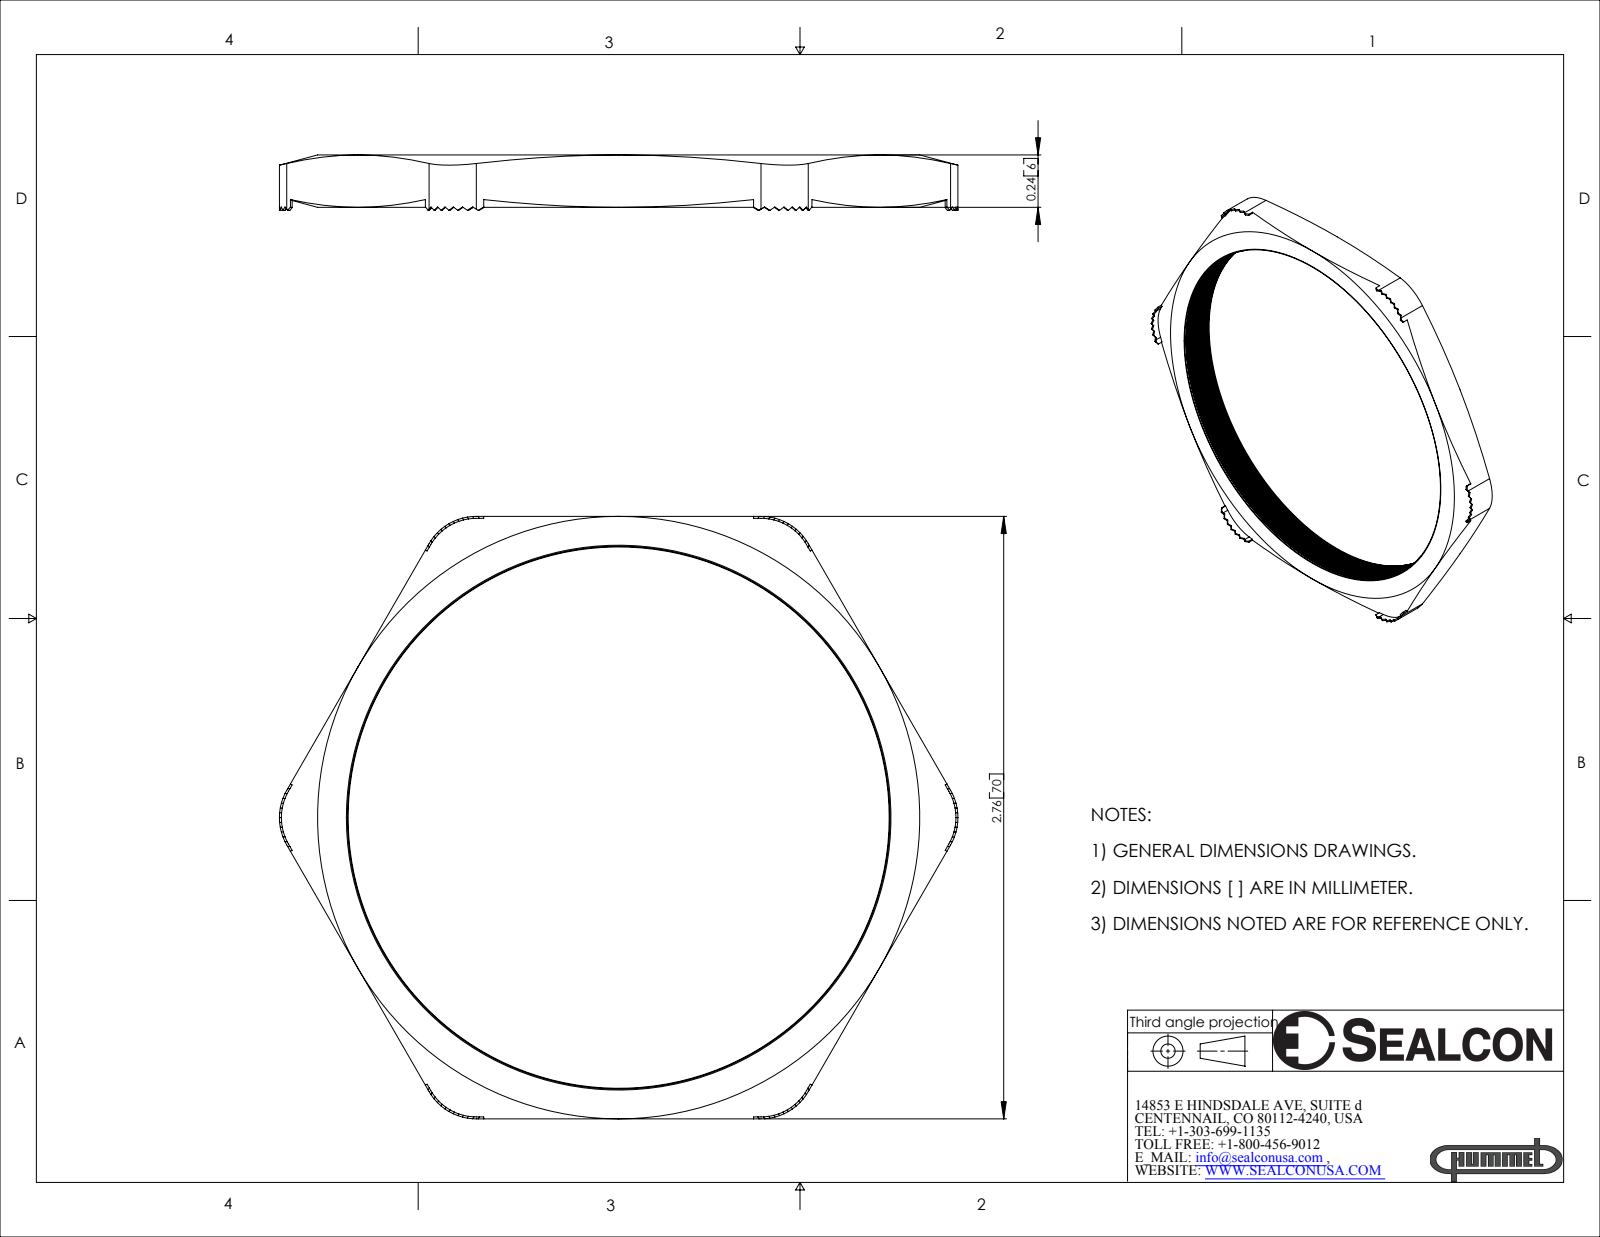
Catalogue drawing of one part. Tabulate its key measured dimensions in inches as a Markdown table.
| quantity | value |
| --- | --- |
| part name | NM-63-BE |
| STEP written by | SolidWorks 2007 (CONFIG_CONTROL_DESIGN) |
| units | inches |
| bodies | 1 solid, 266 faces (116 planar, 52 cylindrical, 98 other) |
| overall size | 3.11 × 2.76 × 0.254 |
| volume | 0.392 in³ |
| surface area | 9.227 in² |
| round holes (diameter × count) | 2.48 × 1 |
| partial cylindrical surfaces (radius × count) | 0.241 × 6, 0.25 × 6 |
| main face-to-face distances | 0.24, 2.76, 2.751, 2.742, 0.051, 0.026, 0.025, 0.076, 0.127, 0.051 |
